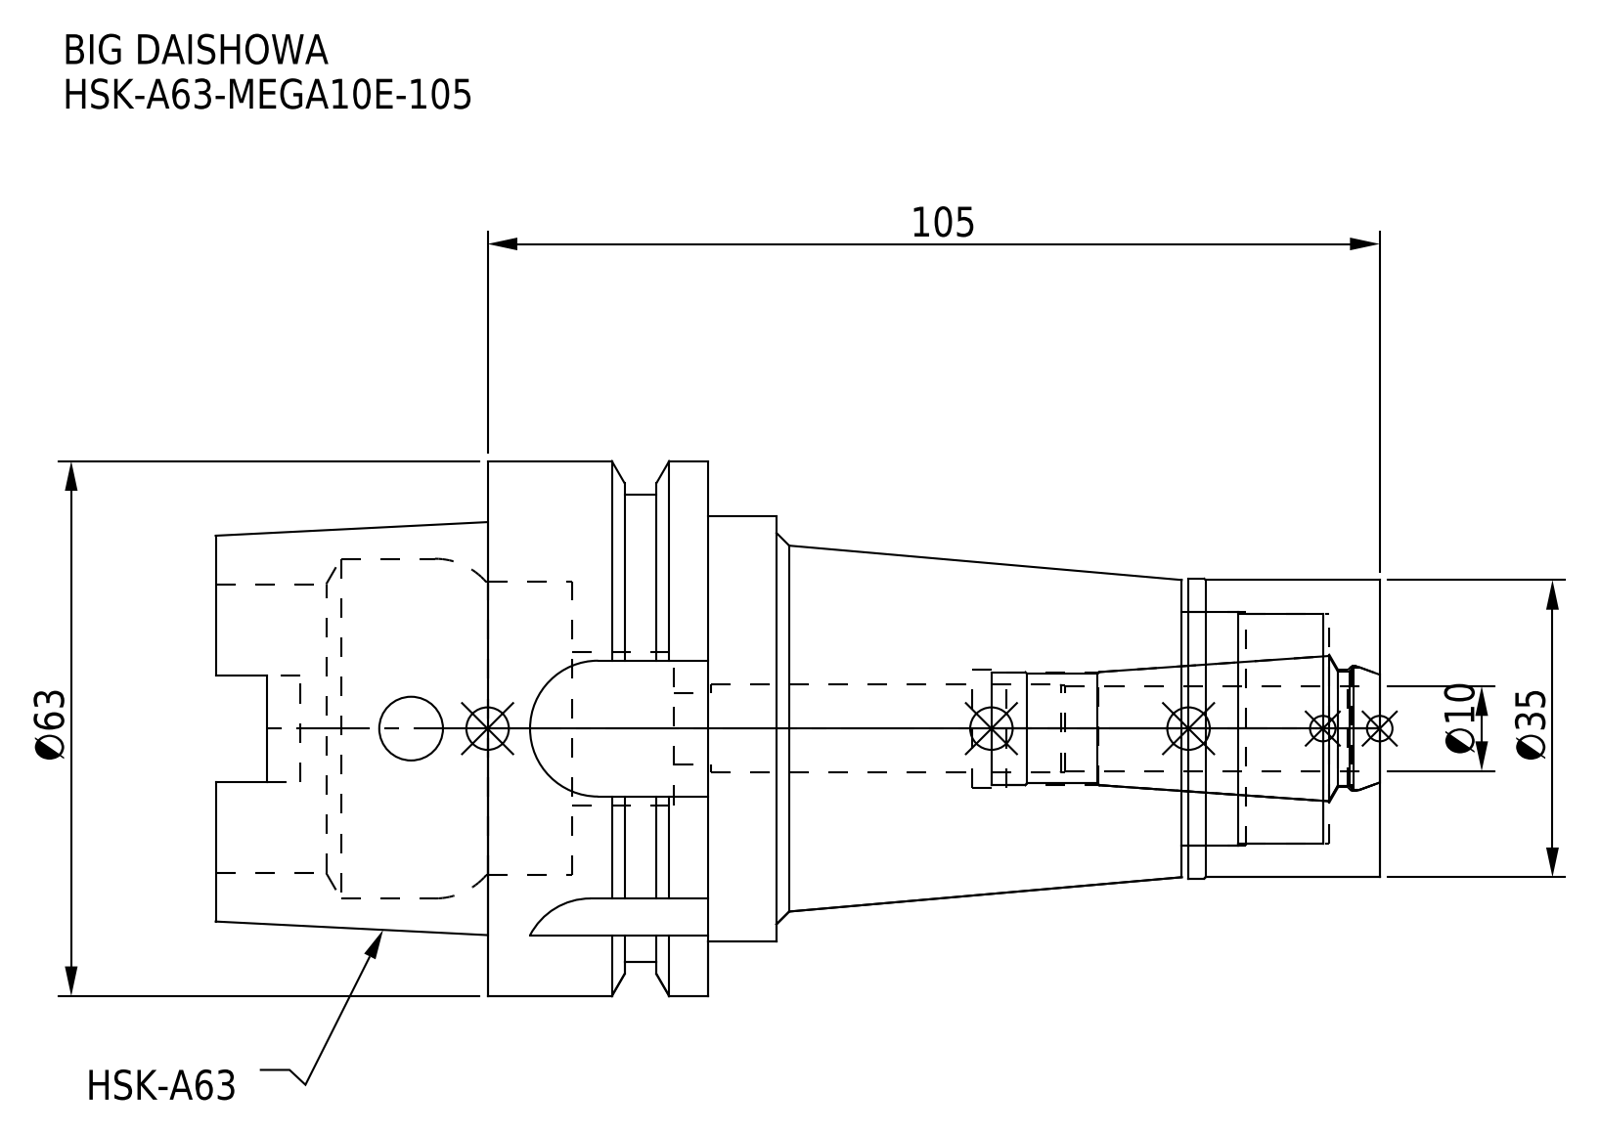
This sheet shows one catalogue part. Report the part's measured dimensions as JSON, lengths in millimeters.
{"part_name": "MEN10_1.stp; HSK-A63-MEGA10E-105-100.stp; HSK-A63-MEGA10E-105-100-FreeParts; HSK-A63-MEGA10E-105 (+3 more)", "step_written_by": "SolidWorks 2019 (CONFIG_CONTROL_DESIGN)", "units": "millimeters", "bodies": {"solids": 2, "faces": 127, "planar": 45, "cylindrical": 54, "other": 28}, "overall_size": [137, 63, 63], "volume_mm3": 166457, "surface_area_mm2": 38911, "round_holes": [[7.5, 1], [8.4, 1], [10.4, 1], [13.3, 1], [13.8, 1], [13.9, 1], [14.7, 1], [18, 1], [27, 1], [27.5, 1], [34, 1], [34.5, 1]], "round_bosses_or_shafts": [[63, 1], [55, 1], [50, 1], [35.3, 1], [35, 1]], "partial_cylinders_radius": [[2.8, 2], [2.88, 2], [8, 2], [9, 1]], "face_to_face_distances": [26, 79, 105, 95.05, 16.05, 9.95, 137, 58, 41.95, 32]}
